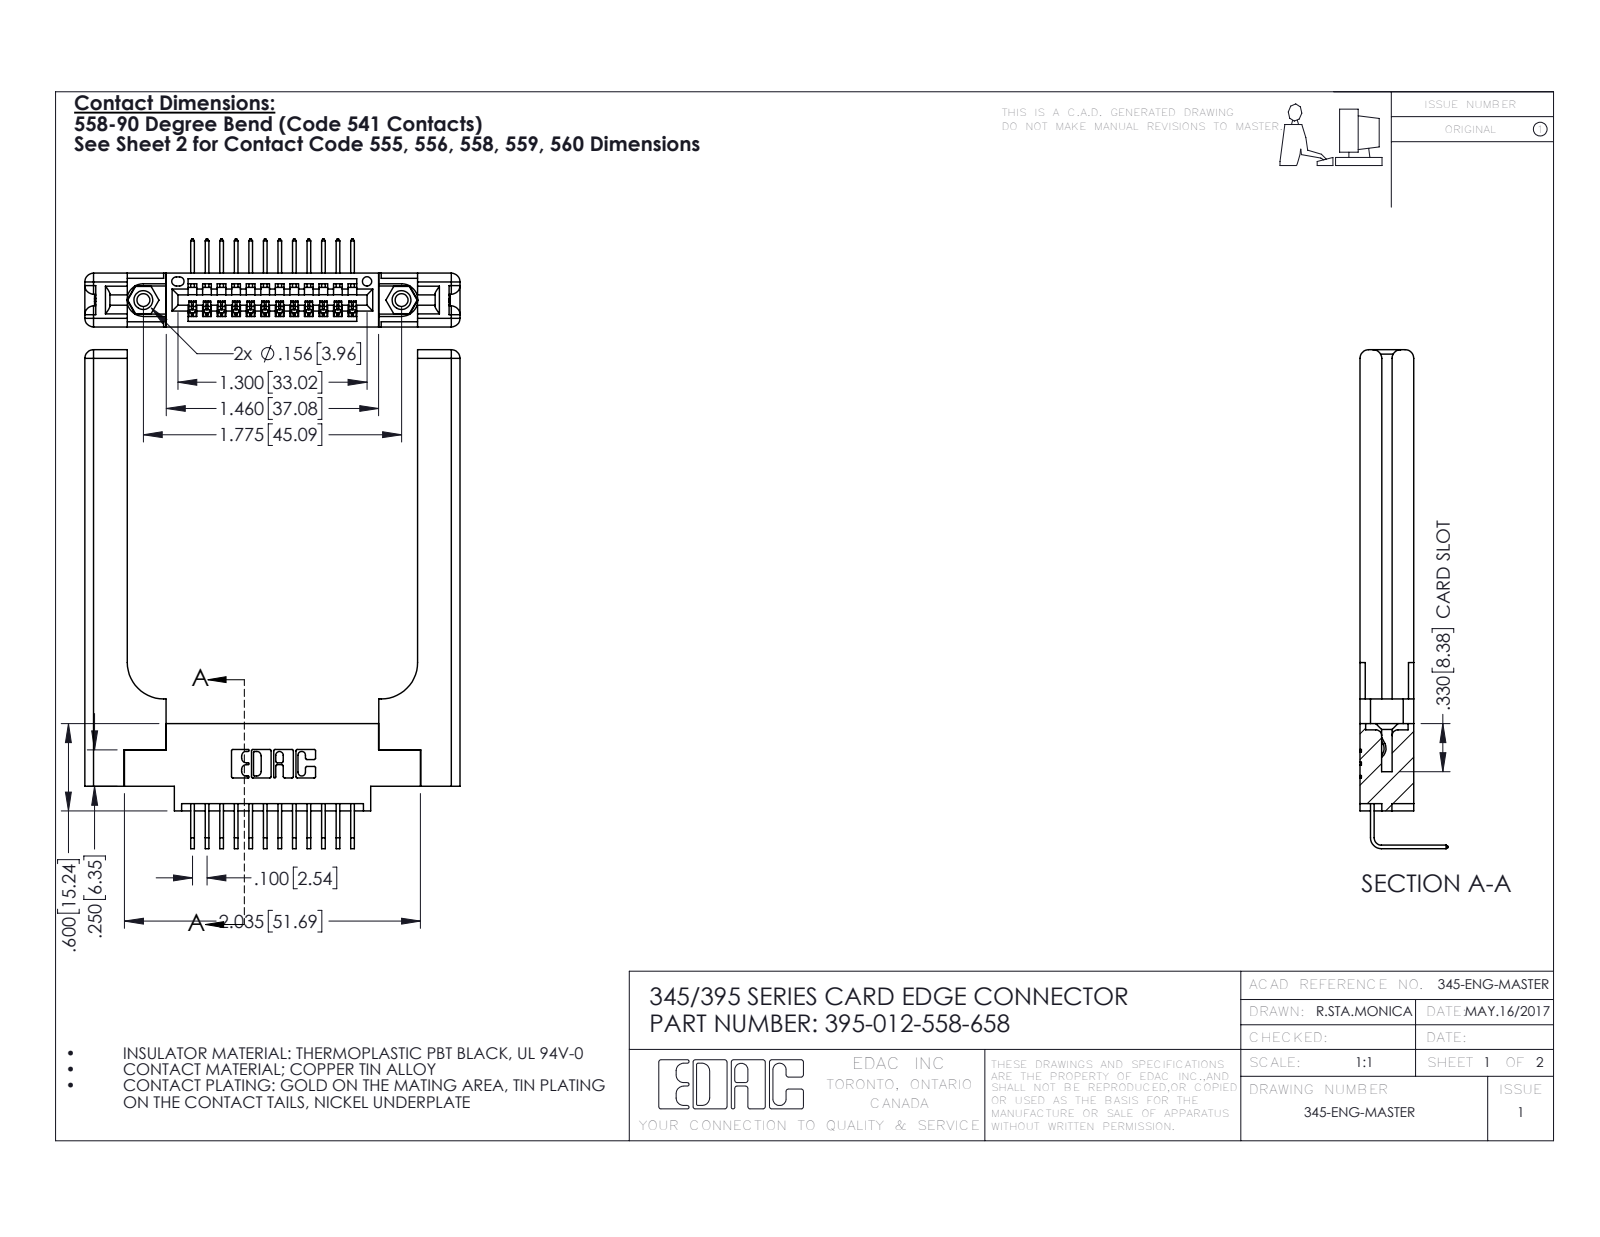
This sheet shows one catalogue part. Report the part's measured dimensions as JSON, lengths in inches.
{"part_name": "345-250-001_345-250-001-102; 345-220-058_345-220-058; 345 Part_0.170 Offset - 0.156 Dia-TH; 395-012-558-658 (+1 more)", "step_written_by": "SolidWorks 2016 (CONFIG_CONTROL_DESIGN)", "units": "inches", "bodies": {"solids": 17, "faces": 1106, "planar": 736, "cylindrical": 310, "other": 60}, "overall_size": [3.429, 2.579, 0.605], "volume_in3": 0.879, "surface_area_in2": 20.31, "round_holes": [[0.089, 2], [0.125, 2], [0.156, 2], [0.064, 1]], "round_bosses_or_shafts": [[0.155, 2]], "partial_cylinders_radius": [[0.006, 24], [0.01, 22], [0.06, 16], [0.007, 6], [0.031, 6], [0.026, 3], [0.03, 2], [0.031, 2]], "face_to_face_distances": [0.37, 0.072, 0.15, 0.22, 0.148, 0.077, 0.298, 1.996, 0.12, 0.071], "hole_center_spacings": [0.27, 1.543, 1.775]}
